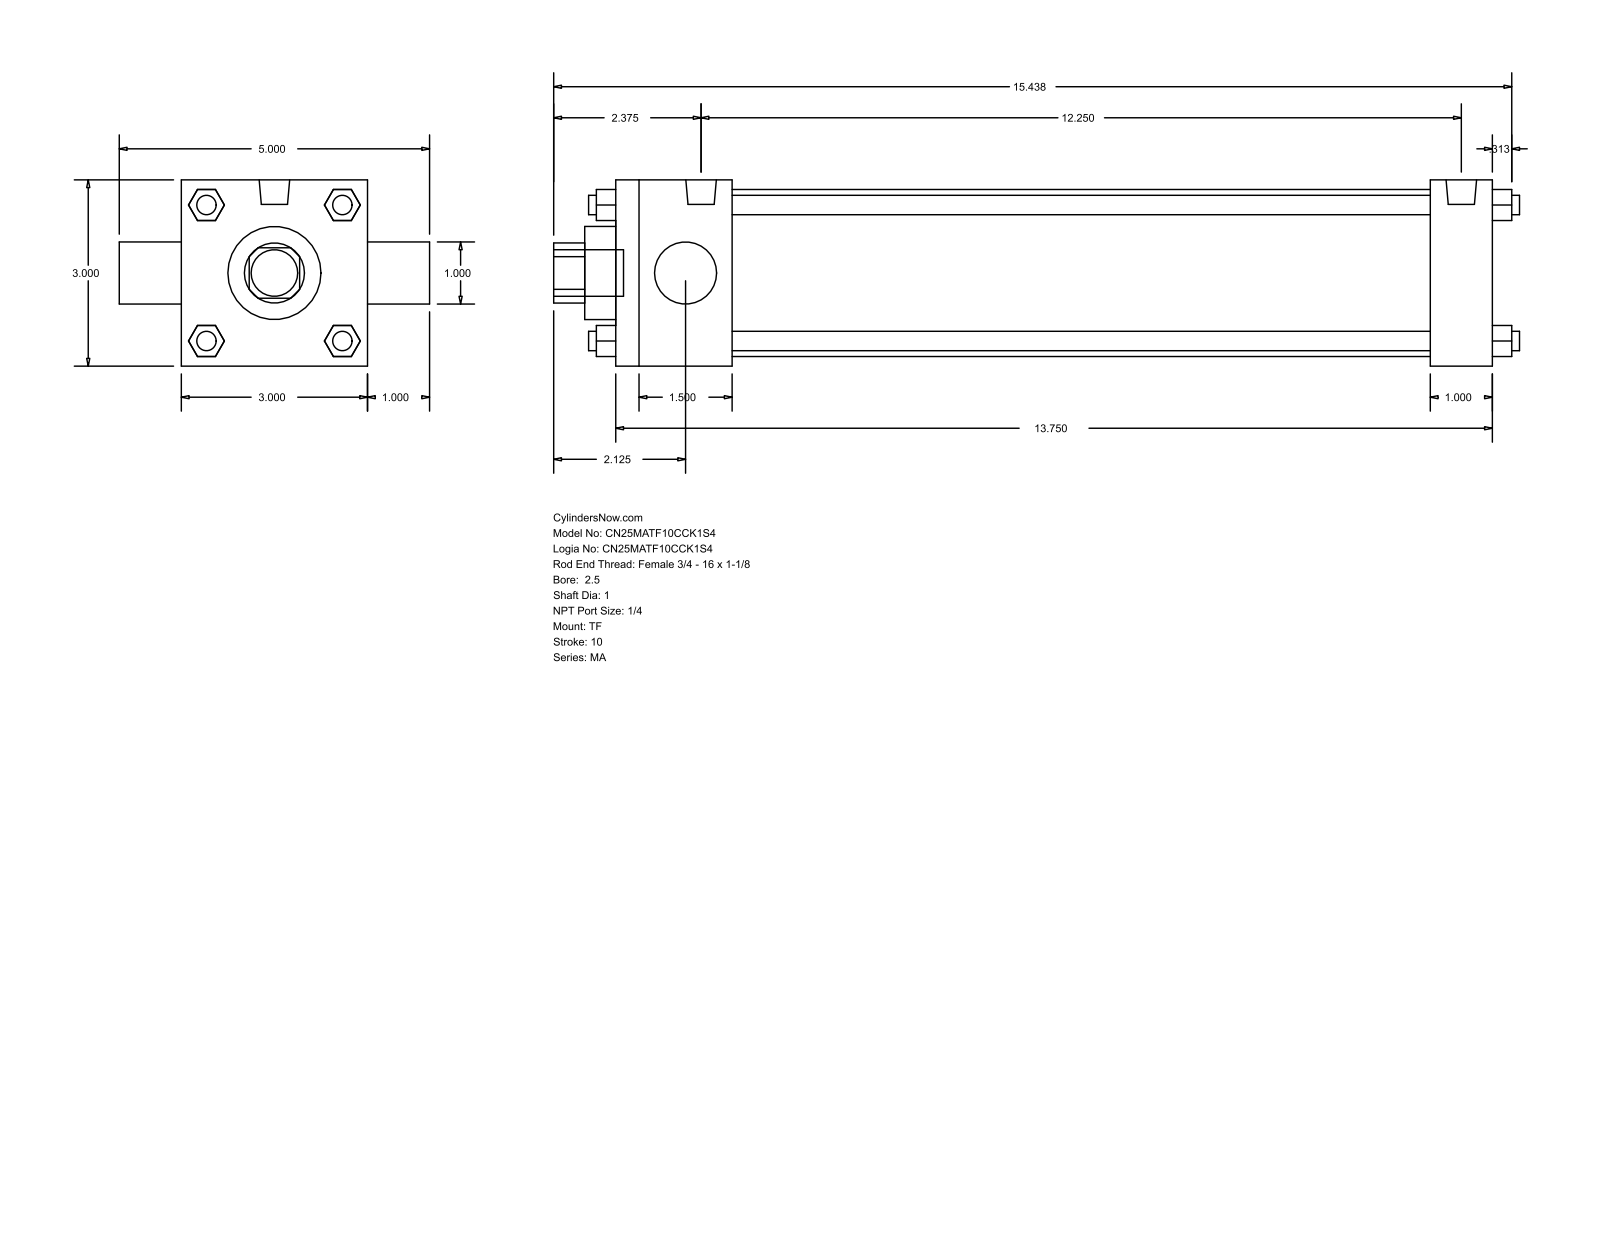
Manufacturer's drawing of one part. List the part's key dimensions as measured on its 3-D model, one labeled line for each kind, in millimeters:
Part name (STEP PRODUCT): MA_TF__0250_1
STEP written by: GSSL Pune (CONFIG_CONTROL_DESIGN)
Units: millimetres
Bodies: 0 solids, 120 faces (92 planar, 28 cylindrical, 0 other)
Overall size (bounding box): 395.29 × 127 × 76.2
Round holes (diameter × count): ⌀25.4 ×2, ⌀38.1 ×1, ⌀68.33 ×1
Round bosses / shafts (diameter × count): ⌀7.94 ×7, ⌀12.49 ×2, ⌀19.05 ×1
Partial cylindrical surfaces — rounded edges, fillets, slot ends (radius × count): R12.29 ×1
Main face-to-face distances: 76.2, 358.78, 12.7, 47.63, 333.37, 285.74, 311.15, 25.41, 25.4, 101.6
